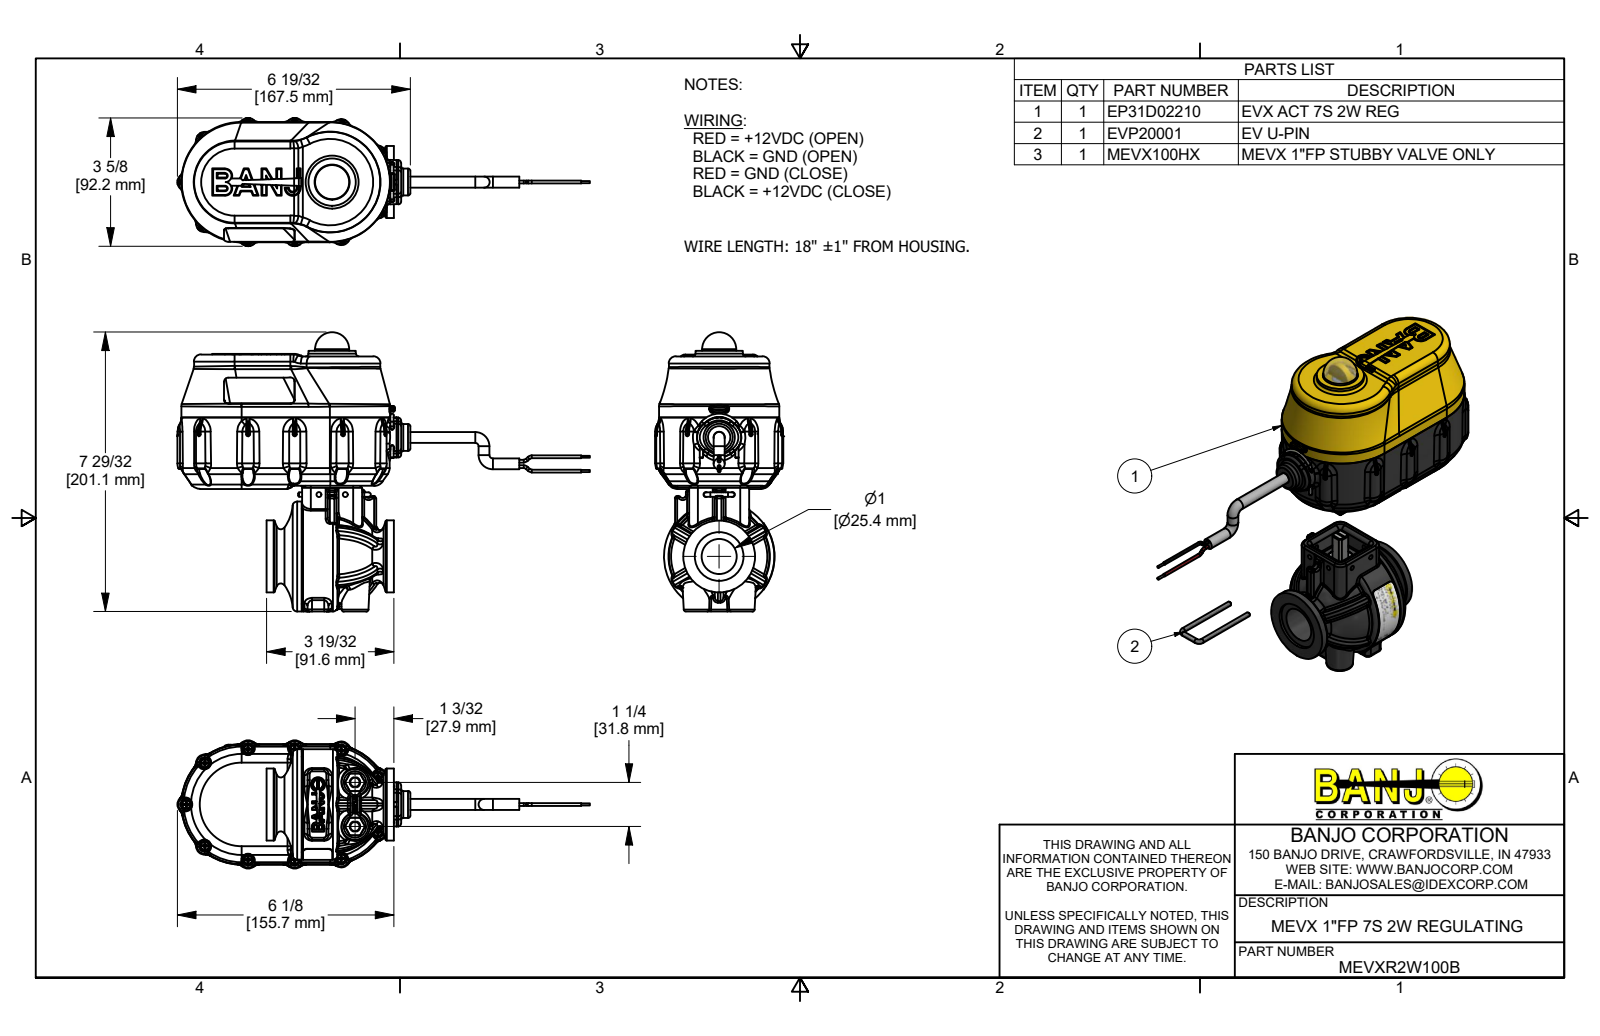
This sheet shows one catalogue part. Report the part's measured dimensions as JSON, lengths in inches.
{"part_name": "MEVXR2W100B; EP31D02210; 91400A119; 95584A200 (+8 more)", "step_written_by": "Autodesk Inventor 2019 (AUTOMOTIVE_DESIGN)", "units": "inches", "bodies": {"solids": 83, "faces": 12215, "planar": 3692, "cylindrical": 3063, "other": 5460}, "overall_size": [11.685, 7.916, 3.63], "volume_in3": 45.34, "surface_area_in2": 526.4, "round_holes": [[0.15, 13], [0.095, 11], [0.135, 5], [0.107, 4], [0.126, 4], [0.136, 4], [0.17, 4], [0.089, 2], [0.105, 2], [0.115, 2], [0.118, 2], [0.123, 2]], "round_bosses_or_shafts": [[0.25, 17], [0.14, 11], [0.108, 11], [0.085, 11], [0.08, 10], [0.27, 4], [0.219, 4], [0.164, 4]], "partial_cylinders_radius": [[0.04, 147], [0.02, 83], [0.01, 56], [0.06, 50], [0.005, 43], [0.08, 28], [0.125, 26], [0.03, 24]], "face_to_face_distances": [0.1, 2.565, 1.685, 0.78, 2.465, 0.88, 0.035, 0.987, 3.005, 0.055], "hole_center_spacings": [1.79, 1.283, 1.662, 2.73, 2.967, 3.45, 0.487, 0.492]}
